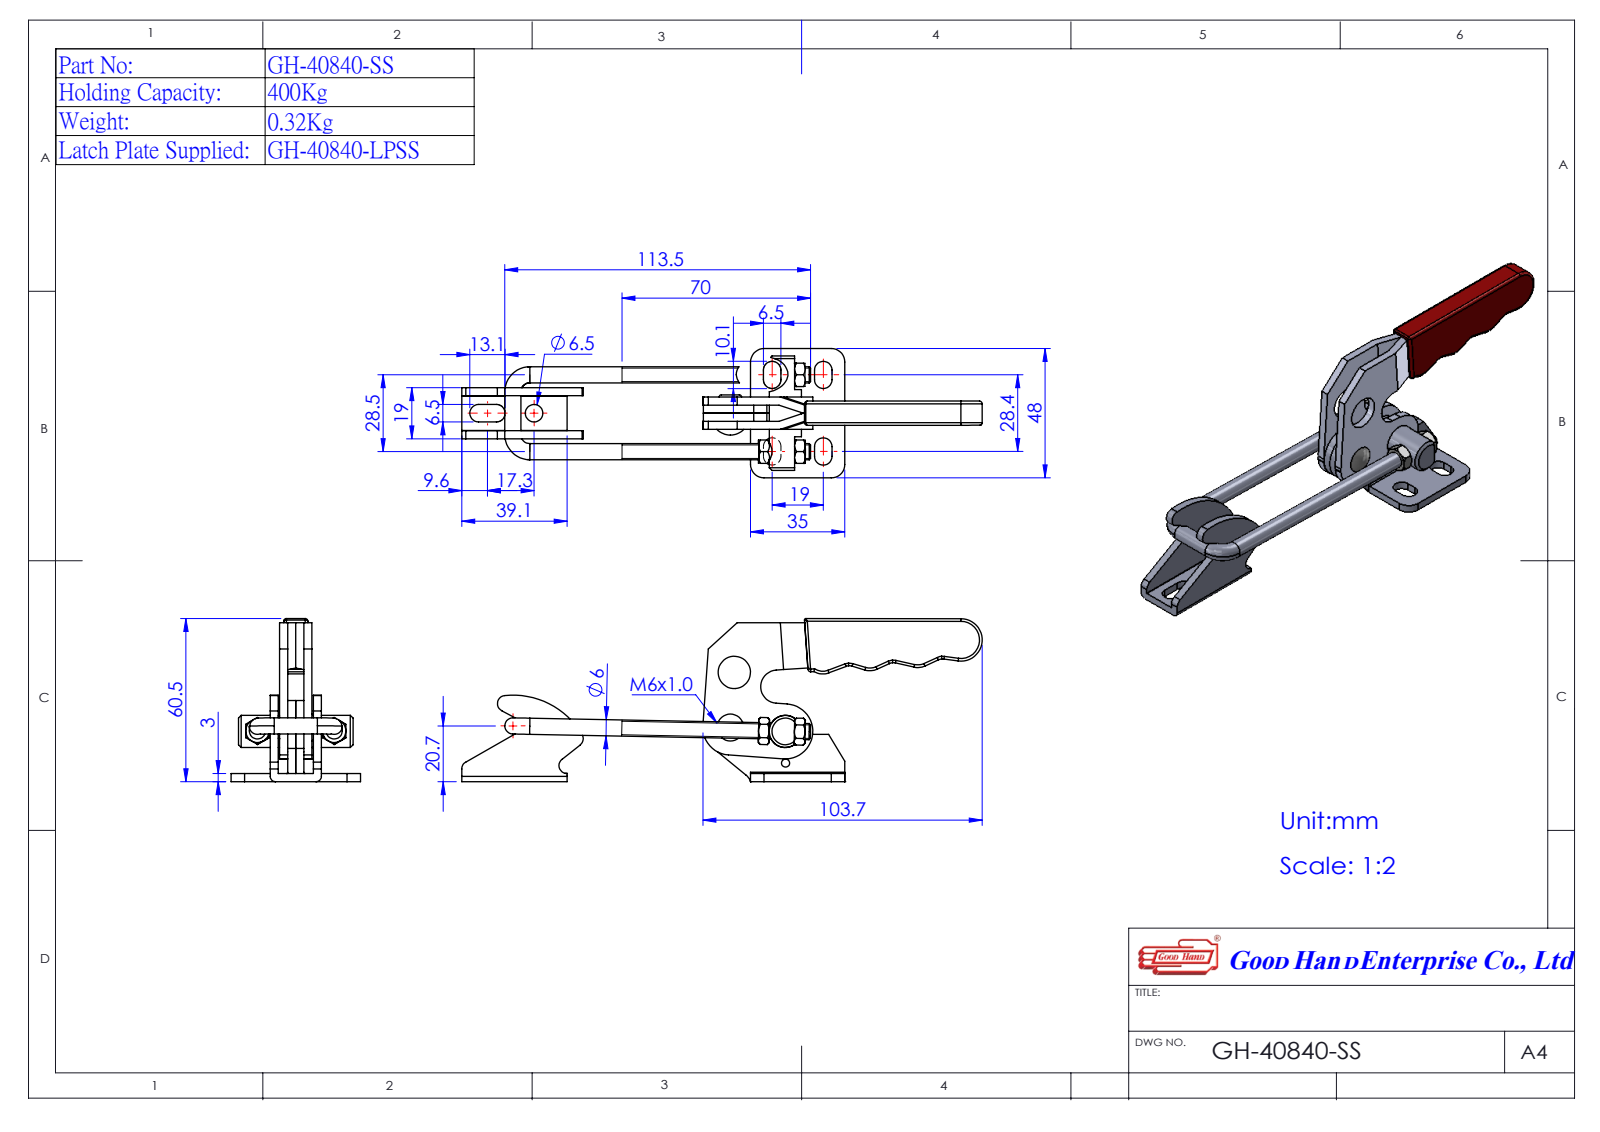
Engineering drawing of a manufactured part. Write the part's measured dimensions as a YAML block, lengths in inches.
part_name: "Group1^GH-40840-SS(簡化); 14084014-1^GH-40840-SS(簡化); Group2^GH-40840-SS(簡化); Group3^GH-40840-SS(簡化) (+2 more)"
step_written_by: "SolidWorks 2016 (AUTOMOTIVE_DESIGN)"
units: inches
bodies: {solids: 5, faces: 261, planar: 126, cylindrical: 102, other: 33}
overall_size: [7.519, 2.383, 1.89]
volume: 2.767
surface_area: 45.29
round_holes:
  - {diameter: 0.236, count: 3}
  - {diameter: 0.472, count: 2}
  - {diameter: 0.098, count: 1}
  - {diameter: 0.197, count: 1}
  - {diameter: 0.256, count: 1}
round_bosses_or_shafts:
  - {diameter: 0.236, count: 2}
  - {diameter: 0.118, count: 1}
partial_cylinders:
  - {radius: 0.128, count: 10}
  - {radius: 0.118, count: 4}
  - {radius: 0.197, count: 4}
  - {radius: 0.138, count: 2}
  - {radius: 0.256, count: 2}
  - {radius: 0.402, count: 2}
  - {radius: 0.02, count: 1}
  - {radius: 0.039, count: 1}
face_to_face_distances: [0.118, 0.059, 0.354, 0.492, 0.138, 0.413, 0.295, 0.236, 0.256, 0.197]
hole_center_spacings: [0.463, 0.805, 0.807, 0.96, 1.122, 1.14, 1.522, 3.091]
